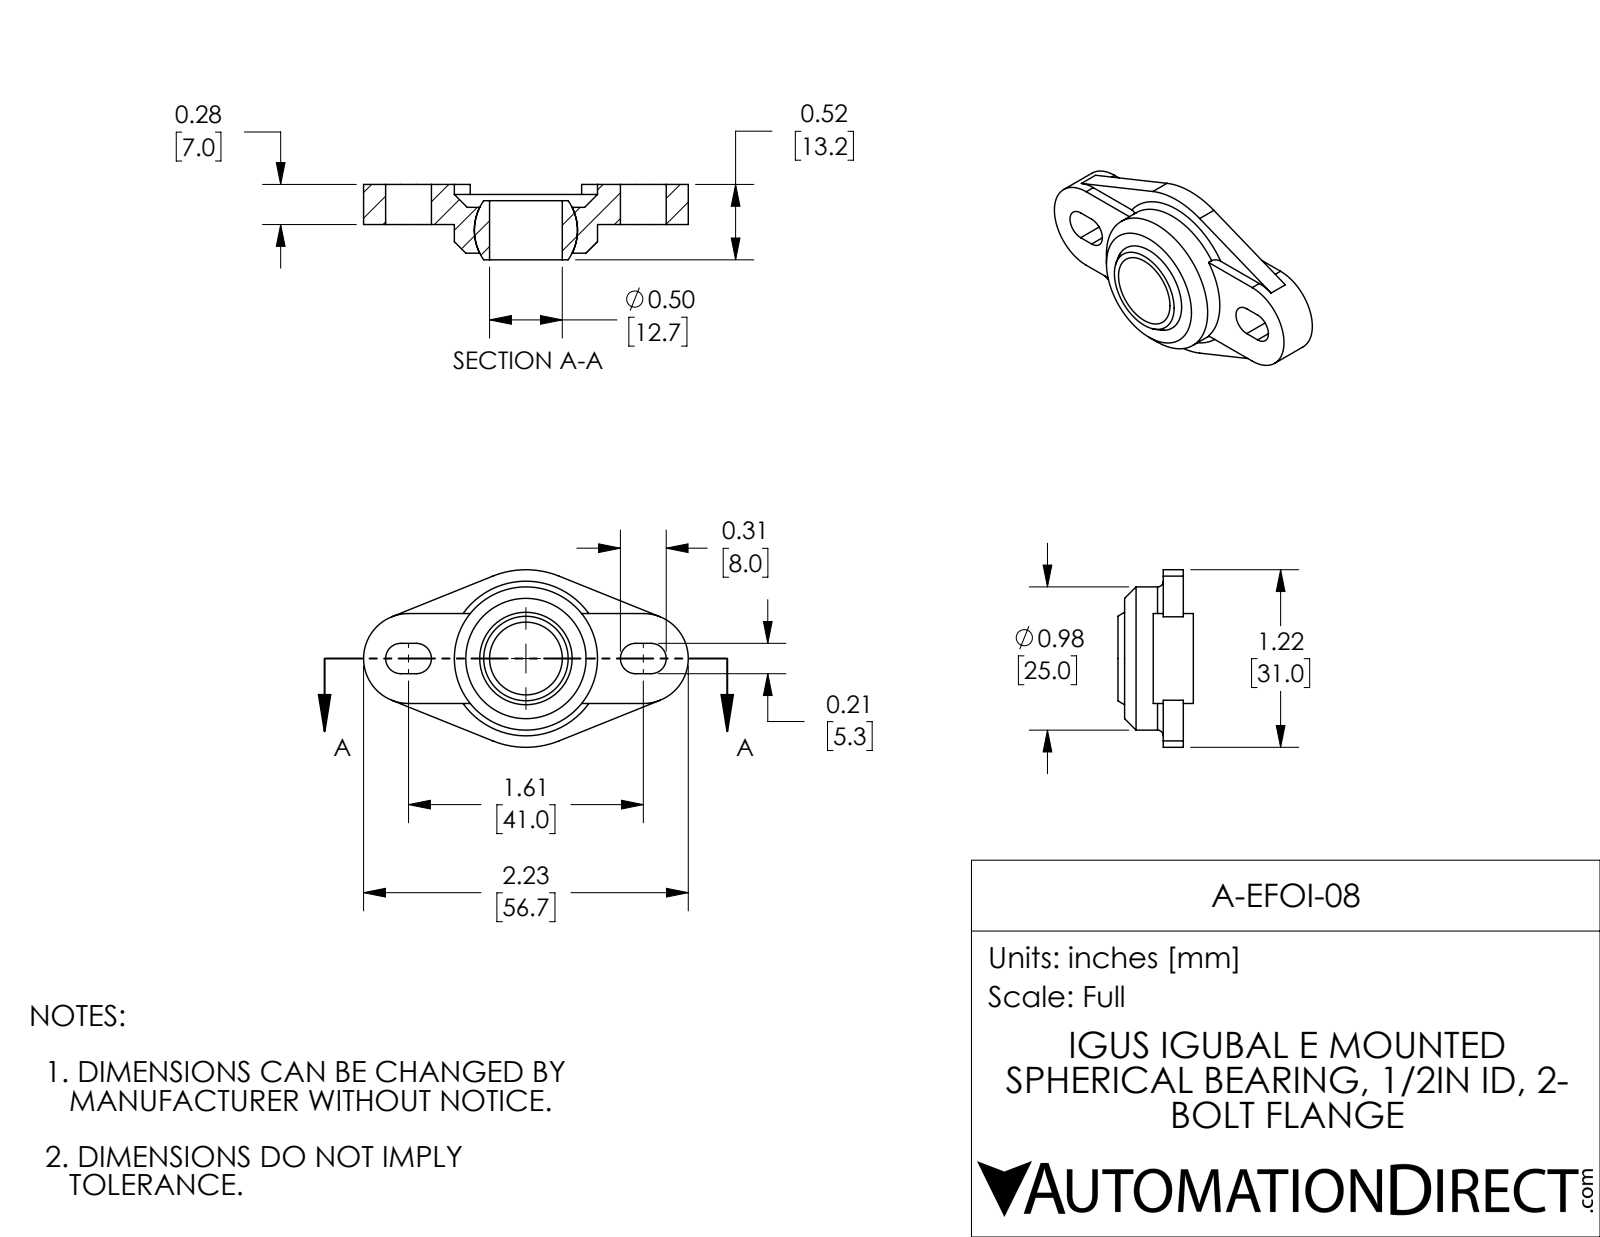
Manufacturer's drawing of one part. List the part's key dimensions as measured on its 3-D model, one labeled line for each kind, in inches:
Part name (STEP PRODUCT): A-EFOI-08
STEP written by: SolidWorks 2017 (AUTOMOTIVE_DESIGN)
Units: inches
Bodies: 2 solids, 56 faces (28 planar, 18 cylindrical, 10 other)
Overall size (bounding box): 2.232 × 1.22 × 0.656
Volume: 0.414 in³ · Surface area: 7.766 in²
Round holes (diameter × count): ⌀0.5 ×1, ⌀0.984 ×1
Partial cylindrical surfaces — rounded edges, fillets, slot ends (radius × count): R0.104 ×4, R0.309 ×2, R0.61 ×1
Main face-to-face distances: 0.069, 0.207, 0.276, 0.138, 0.472, 0.404, 0.266, 0.197, 1.22, 0.157
